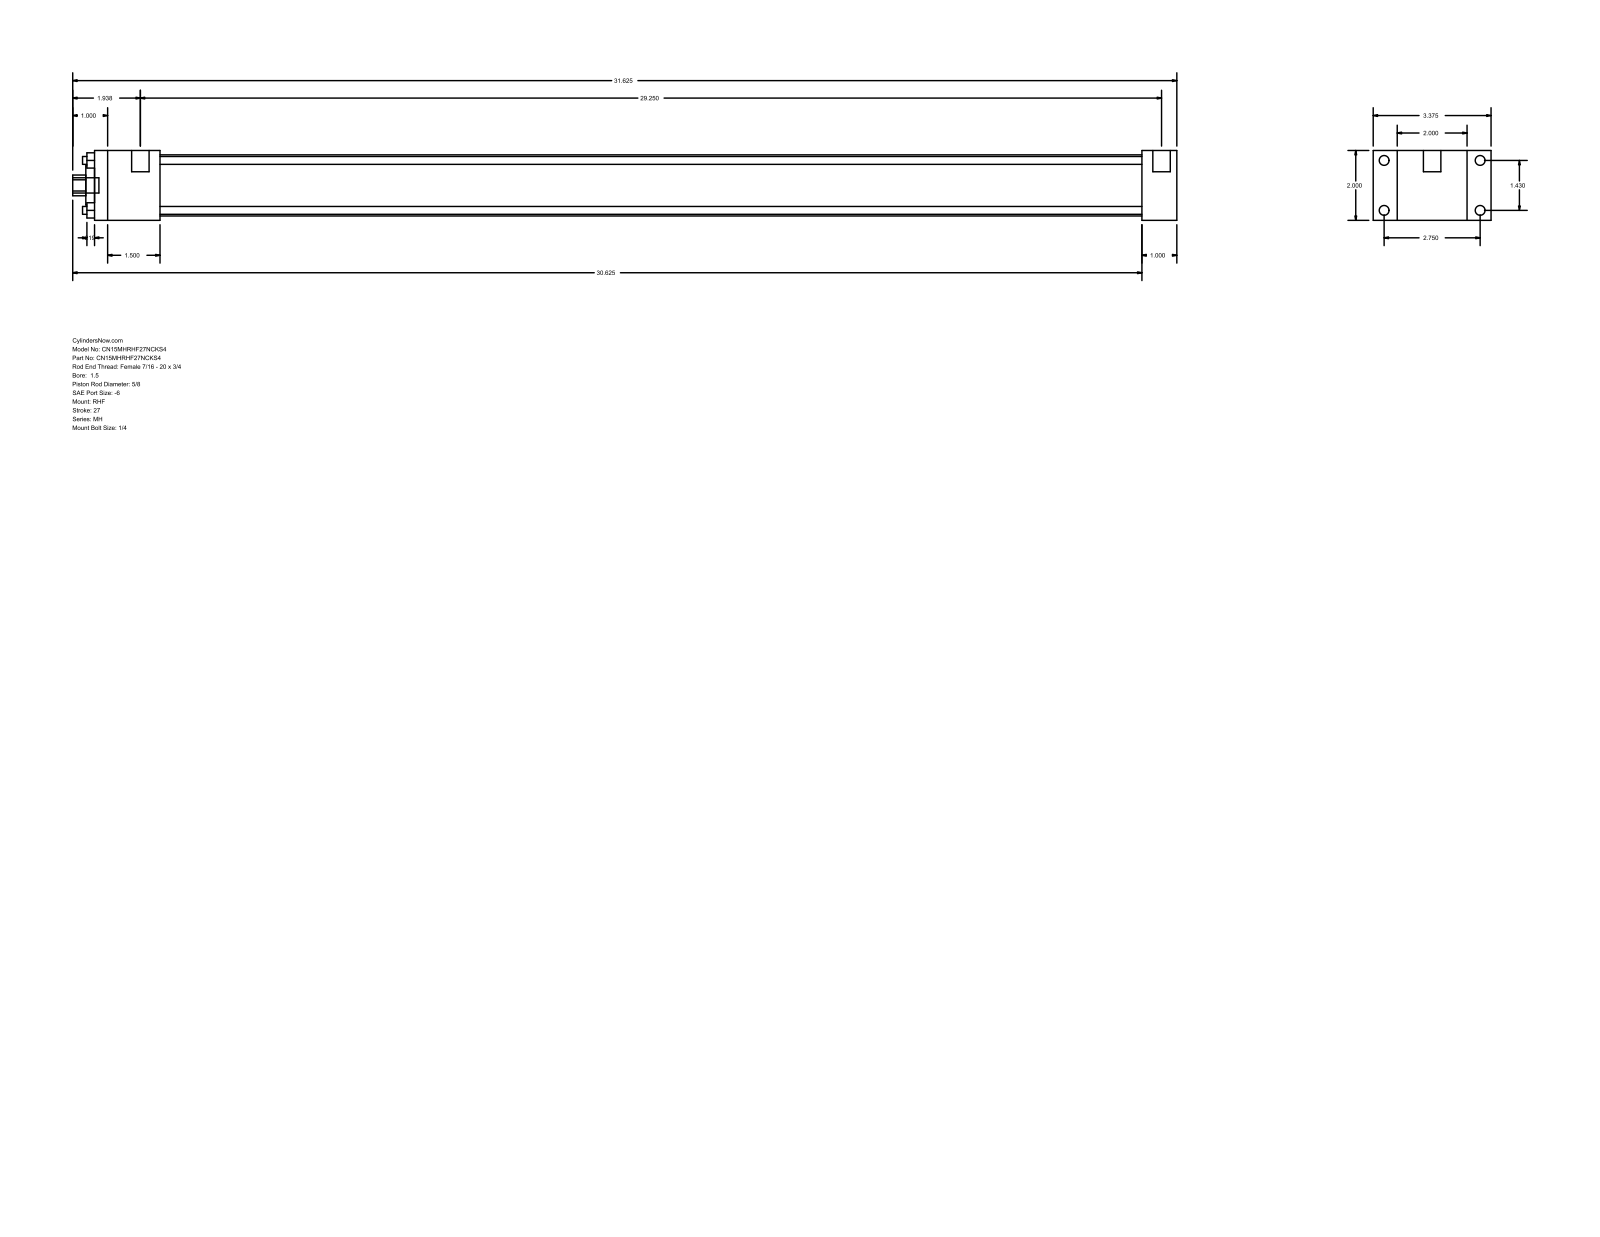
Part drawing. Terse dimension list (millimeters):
name: MH_RHF__0150_0.625
written by: GSSL Pune (CONFIG_CONTROL_DESIGN)
unit: mm
bodies: 0 solids, 88 faces (60 planar, 28 cylindrical, 0 other)
size: 803.27 × 85.72 × 50.8
holes: 4× ⌀5.71, 1× ⌀15.88, 1× ⌀28.57, 1× ⌀44.45
bosses: 4× ⌀7.14, 4× ⌀5.56, 2× ⌀12.7, 1× ⌀11.11
rounds: 1× R7.54
face distances: 50.8, 17.46, 68.26, 25.39, 762, 787.39, 85.72, 47.62, 714.38, 739.77
hole spacings: 25.68, 36.32, 51.36
